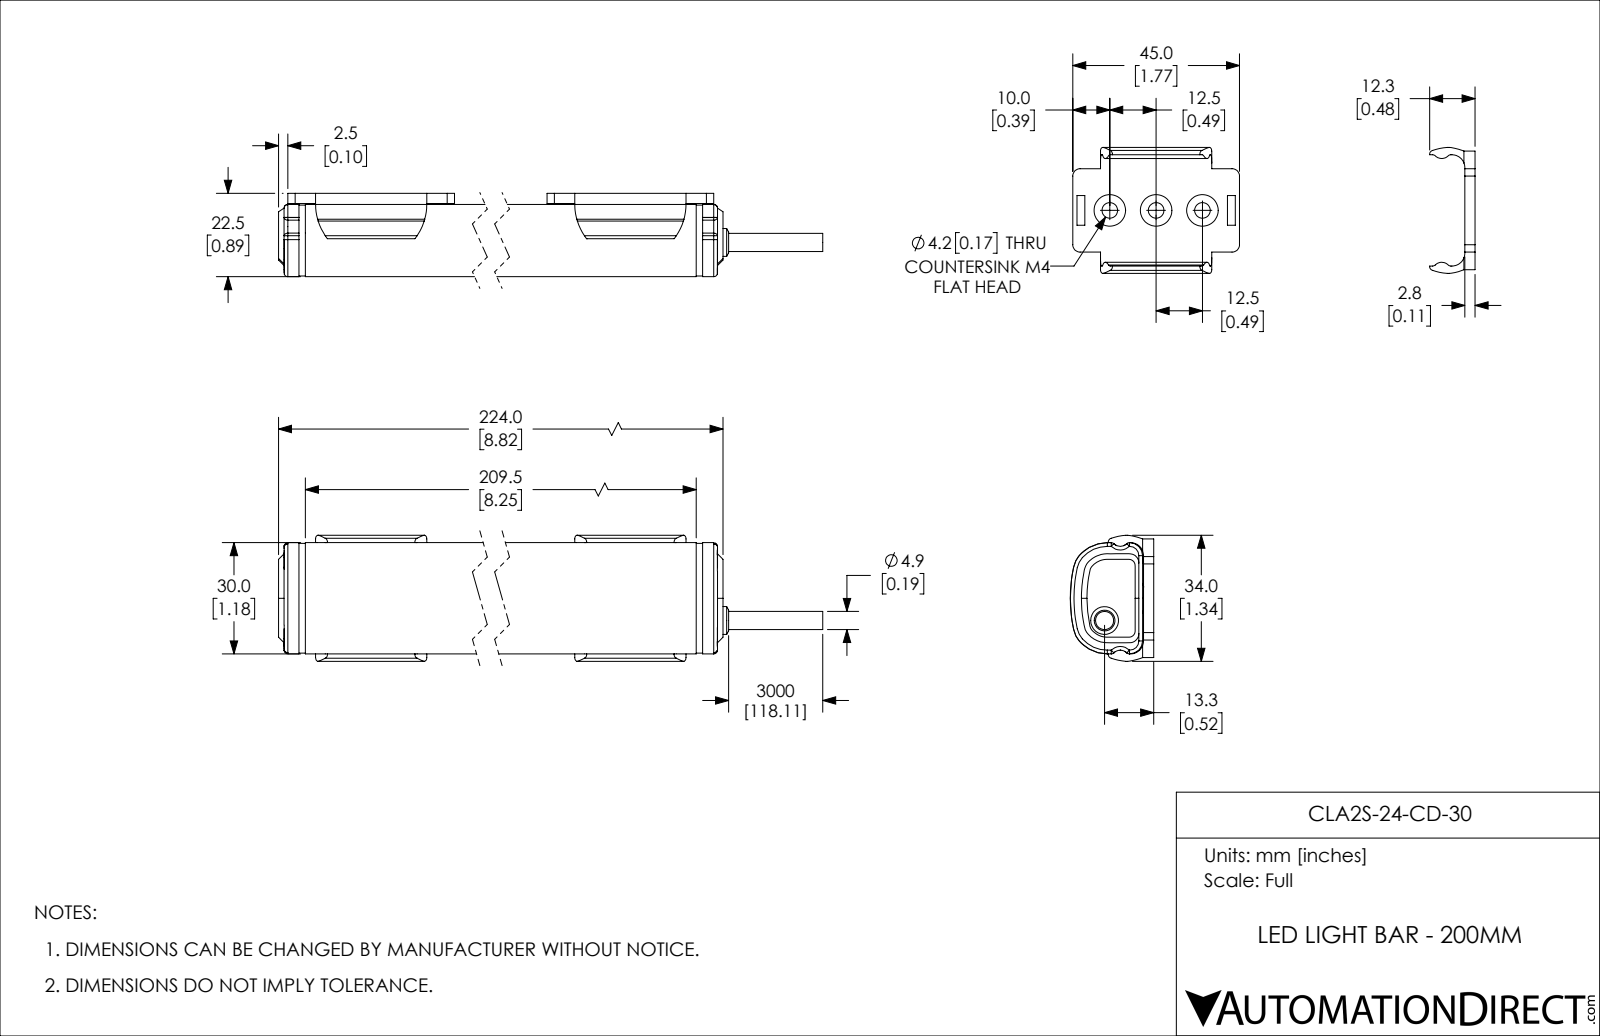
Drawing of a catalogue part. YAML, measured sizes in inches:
part_name: "CLA2S-24-CD-30"
step_written_by: "SolidWorks 2018 (AUTOMOTIVE_DESIGN)"
units: inches
bodies: {solids: 3, faces: 208, planar: 57, cylindrical: 93, other: 58}
overall_size: [9.878, 1.339, 0.886]
volume: 7.725
surface_area: 45.37
round_holes:
  - {diameter: 0.165, count: 6}
  - {diameter: 0.335, count: 6}
round_bosses_or_shafts:
  - {diameter: 0.295, count: 1}
  - {diameter: 0.193, count: 1}
partial_cylinders:
  - {radius: 0.039, count: 10}
  - {radius: 0.079, count: 8}
  - {radius: 0.591, count: 6}
  - {radius: 0.098, count: 2}
  - {radius: 0.138, count: 2}
  - {radius: 0.433, count: 1}
face_to_face_distances: [8.819, 0.059, 8.76, 1.26, 0.039, 6.85, 0.118, 0.187, 1.073, 0.295]
hole_center_spacings: [0.492, 6.85, 0.984, 6.358, 7.343, 5.866, 7.835]
